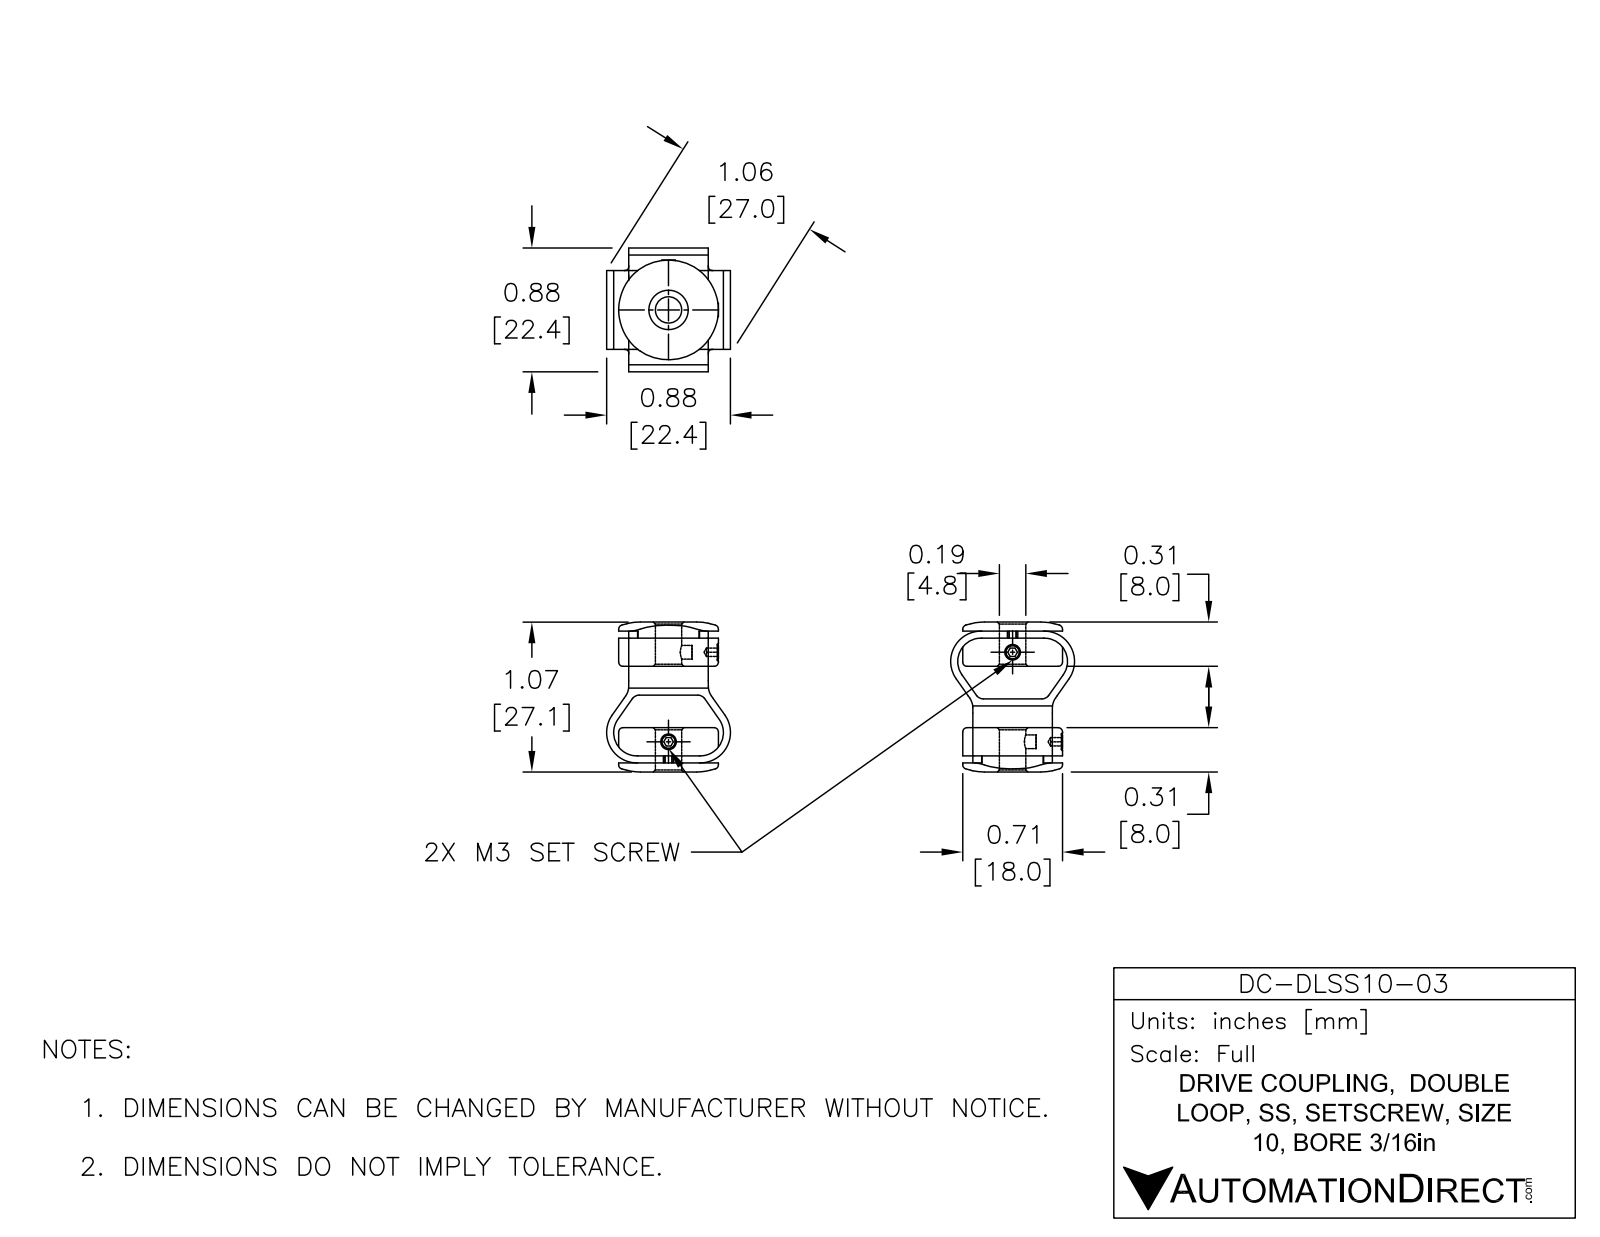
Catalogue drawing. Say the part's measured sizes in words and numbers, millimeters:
The part is named "DC-DLSS10-03". Its 3-D file was written by "SolidWorks 2015 (AUTOMOTIVE_DESIGN)". It is 1 solid with 110 faces: 57 planar, 28 cylindrical and 25 other. Overall it measures 33.4 by 22.35 by 22.35 millimeters. Its volume is 4 340 cubic millimeters and its surface area 3 946 square millimeters. Round holes: 1 of diameter 4.76. Round bosses or shafts: 1 of diameter 18.01. Partial cylindrical surfaces (rounded edges, fillets, slot ends): 4 of radius 4.19, 4 of radius 5.46, 1 of radius 5.59. The main face-to-face distances are 1.27, 33.4, 16.38, 17.02, 17.65, 15.75, 7.06, 26.34, 12.23, 11.6.
